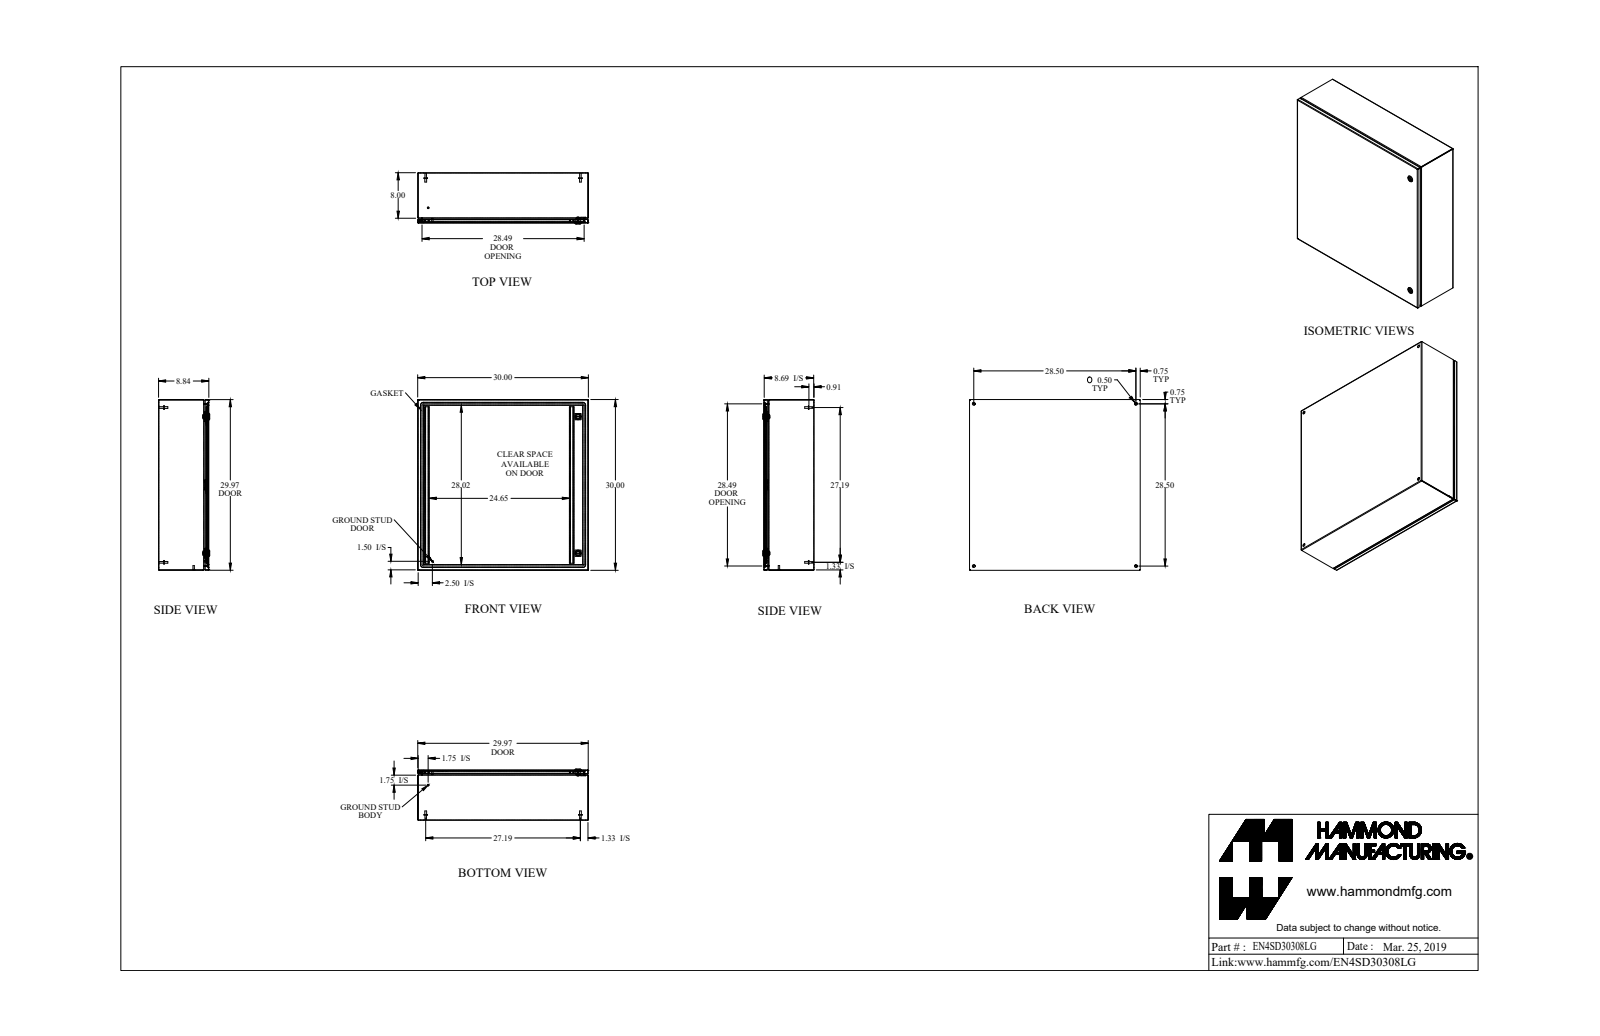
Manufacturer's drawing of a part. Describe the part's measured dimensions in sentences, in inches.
The part is named "EN4SD30308LG_Default". Its 3-D file was written by "SolidWorks 2019 (CONFIG_CONTROL_DESIGN)". It is 31 solids with 885 faces: 422 planar, 295 cylindrical and 168 other. Overall it measures 30 by 30 by 8.997 inches. Its volume is 231 cubic inches and its surface area 6 467 square inches. Round holes: 4 of diameter 0.5, 2 of diameter 0.232, 2 of diameter 0.625, 2 of diameter 0.785, 1 of diameter 0.172, 1 of diameter 0.24, 1 of diameter 0.242. Round bosses or shafts: 4 of diameter 0.625, 4 of diameter 0.313, 4 of diameter 0.27, 2 of diameter 1.1, 2 of diameter 0.525, 2 of diameter 0.281, 2 of diameter 0.25, 1 of diameter 0.455. Partial cylindrical surfaces (rounded edges, fillets, slot ends): 20 of radius 0.036, 20 of radius 0.108, 12 of radius 0.043, 12 of radius 0.081, 12 of radius 0.382, 8 of radius 19.003, 6 of radius 0.006, 6 of radius 0.062. The main face-to-face distances are 0.072, 8.765, 29.928, 8.693, 8.837, 29.856, 30, 0.837, 7.928, 0.75. The hole center spacings are 28.5, 2.493, 26.272, 27.519, 37.964, 40.305, 23.999.
